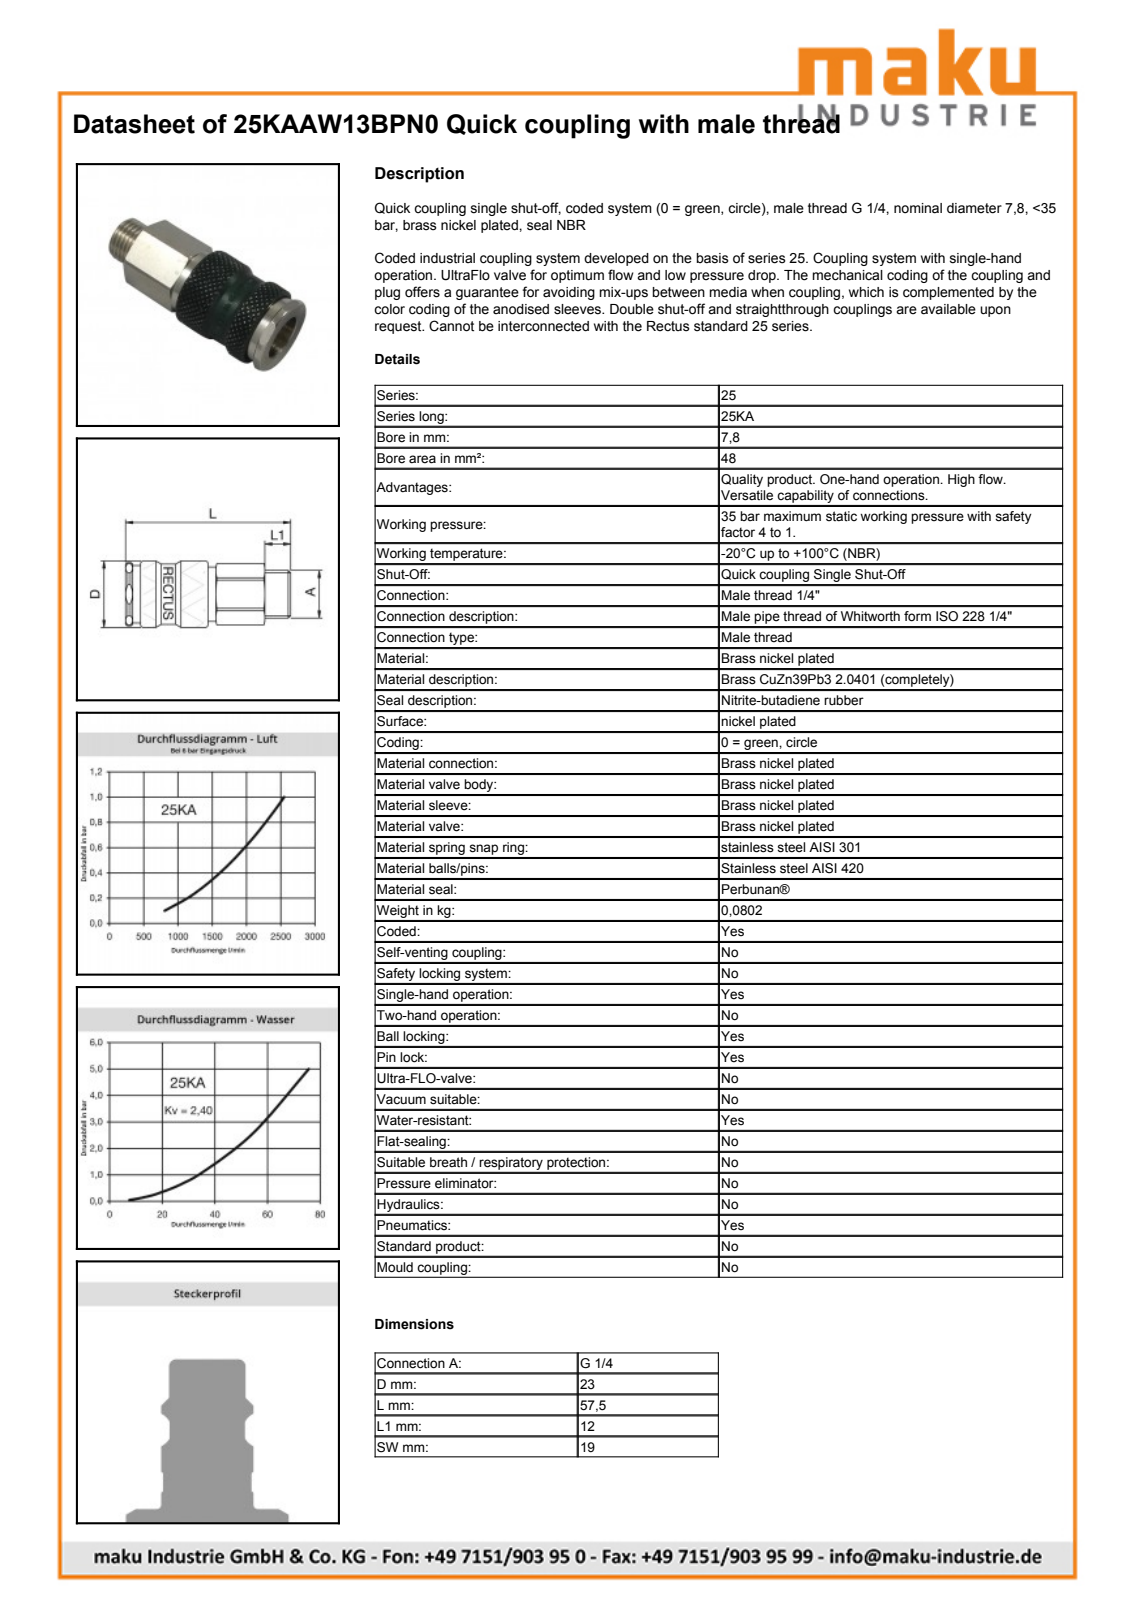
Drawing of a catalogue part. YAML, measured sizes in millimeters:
part_name: "D106597"
step_written_by: "Autodesk Inventor 2011 (AUTOMOTIVE_DESIGN)"
units: millimeters
bodies: {solids: 2, faces: 738, planar: 252, cylindrical: 86, other: 400}
overall_size: [57.5, 23.15, 23.15]
volume: 17024
surface_area: 8029
round_holes:
  - {diameter: 15.1, count: 1}
  - {diameter: 16, count: 1}
  - {diameter: 17.25, count: 1}
  - {diameter: 19.35, count: 1}
  - {diameter: 20.05, count: 1}
round_bosses_or_shafts:
  - {diameter: 23.15, count: 1}
  - {diameter: 21, count: 1}
  - {diameter: 20, count: 1}
  - {diameter: 18.95, count: 1}
  - {diameter: 15.3, count: 1}
  - {diameter: 15, count: 1}
  - {diameter: 14.59, count: 1}
  - {diameter: 13.16, count: 1}
partial_cylinders:
  - {radius: 7.9, count: 1}
  - {radius: 10.4, count: 1}
  - {radius: 10.7, count: 1}
  - {radius: 11, count: 1}
face_to_face_distances: [19, 48.5, 57.5, 9, 24.5, 24, 33, 19.8, 28.7, 4.2]
